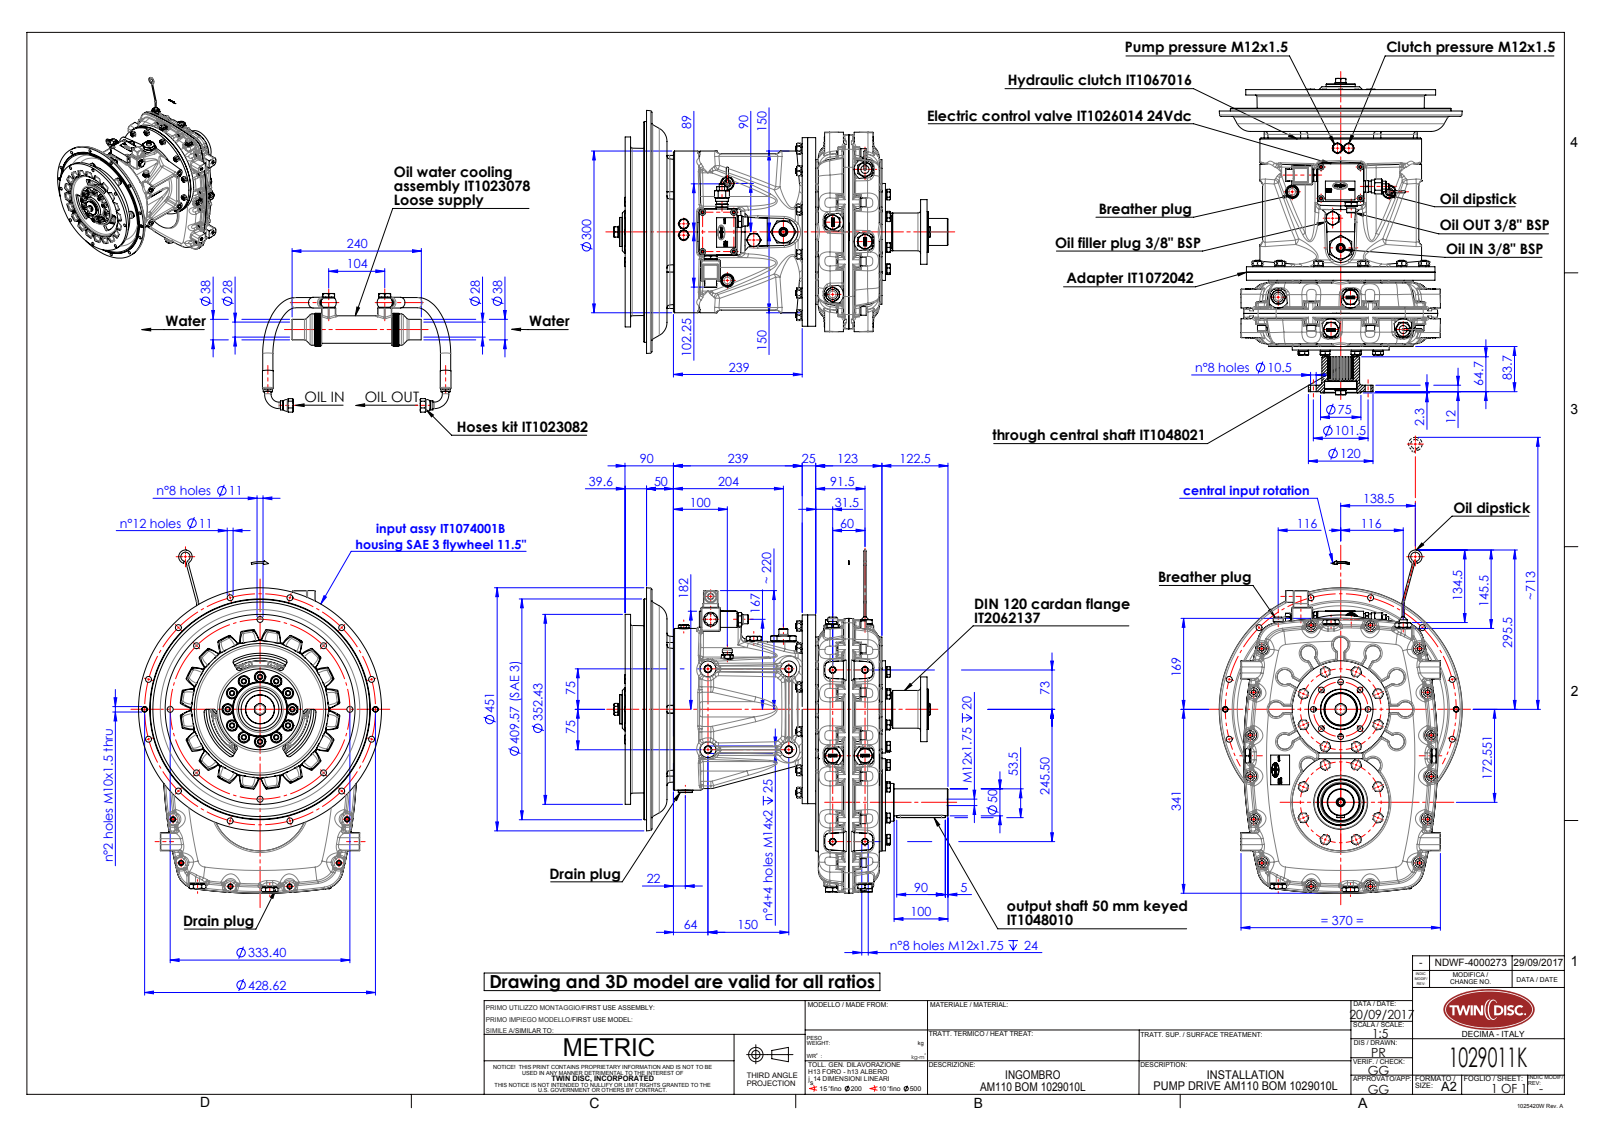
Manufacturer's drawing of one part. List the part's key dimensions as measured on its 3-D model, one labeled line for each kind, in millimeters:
Part name (STEP PRODUCT): IT1054018_rev00-installation; IT1048010_rev01-installation; IT1023082-installation; ITam220-018_rev00-installation (+8 more)
STEP written by: SolidWorks 2015 (AUTOMOTIVE_DESIGN)
Units: millimetres
Bodies: 26 solids, 12609 faces (4849 planar, 2893 cylindrical, 4867 other)
Overall size (bounding box): 1012.1 × 899.51 × 636.78
Volume: 8 322 000 mm³ · Surface area: 4 052 000 mm²
Round holes (diameter × count): ⌀11 ×78, ⌀10.2 ×69, ⌀8.5 ×65, ⌀10.5 ×26, ⌀14 ×16, ⌀12.5 ×15, ⌀15 ×13, ⌀12 ×11, ⌀18.63 ×10, ⌀13 ×9, ⌀21 ×9, ⌀20 ×8
Round bosses / shafts (diameter × count): ⌀10 ×73, ⌀16.2 ×37, ⌀18.1 ×28, ⌀12 ×23, ⌀21 ×19, ⌀16.1 ×16, ⌀16 ×16, ⌀24 ×12
Partial cylindrical surfaces — rounded edges, fillets, slot ends (radius × count): R3 ×168, R0.35 ×104, R1 ×98, R4 ×80, R5 ×58, R29.53 ×58, R2.5 ×50, R18.49 ×46
Main face-to-face distances: 10, 20, 61.5, 76.5, 5, 86.5, 123, 269, 289, 25
Hole centre spacings: 120, 207.84, 231.82, 330, 51.37, 123.96, 157.1, 169.7
